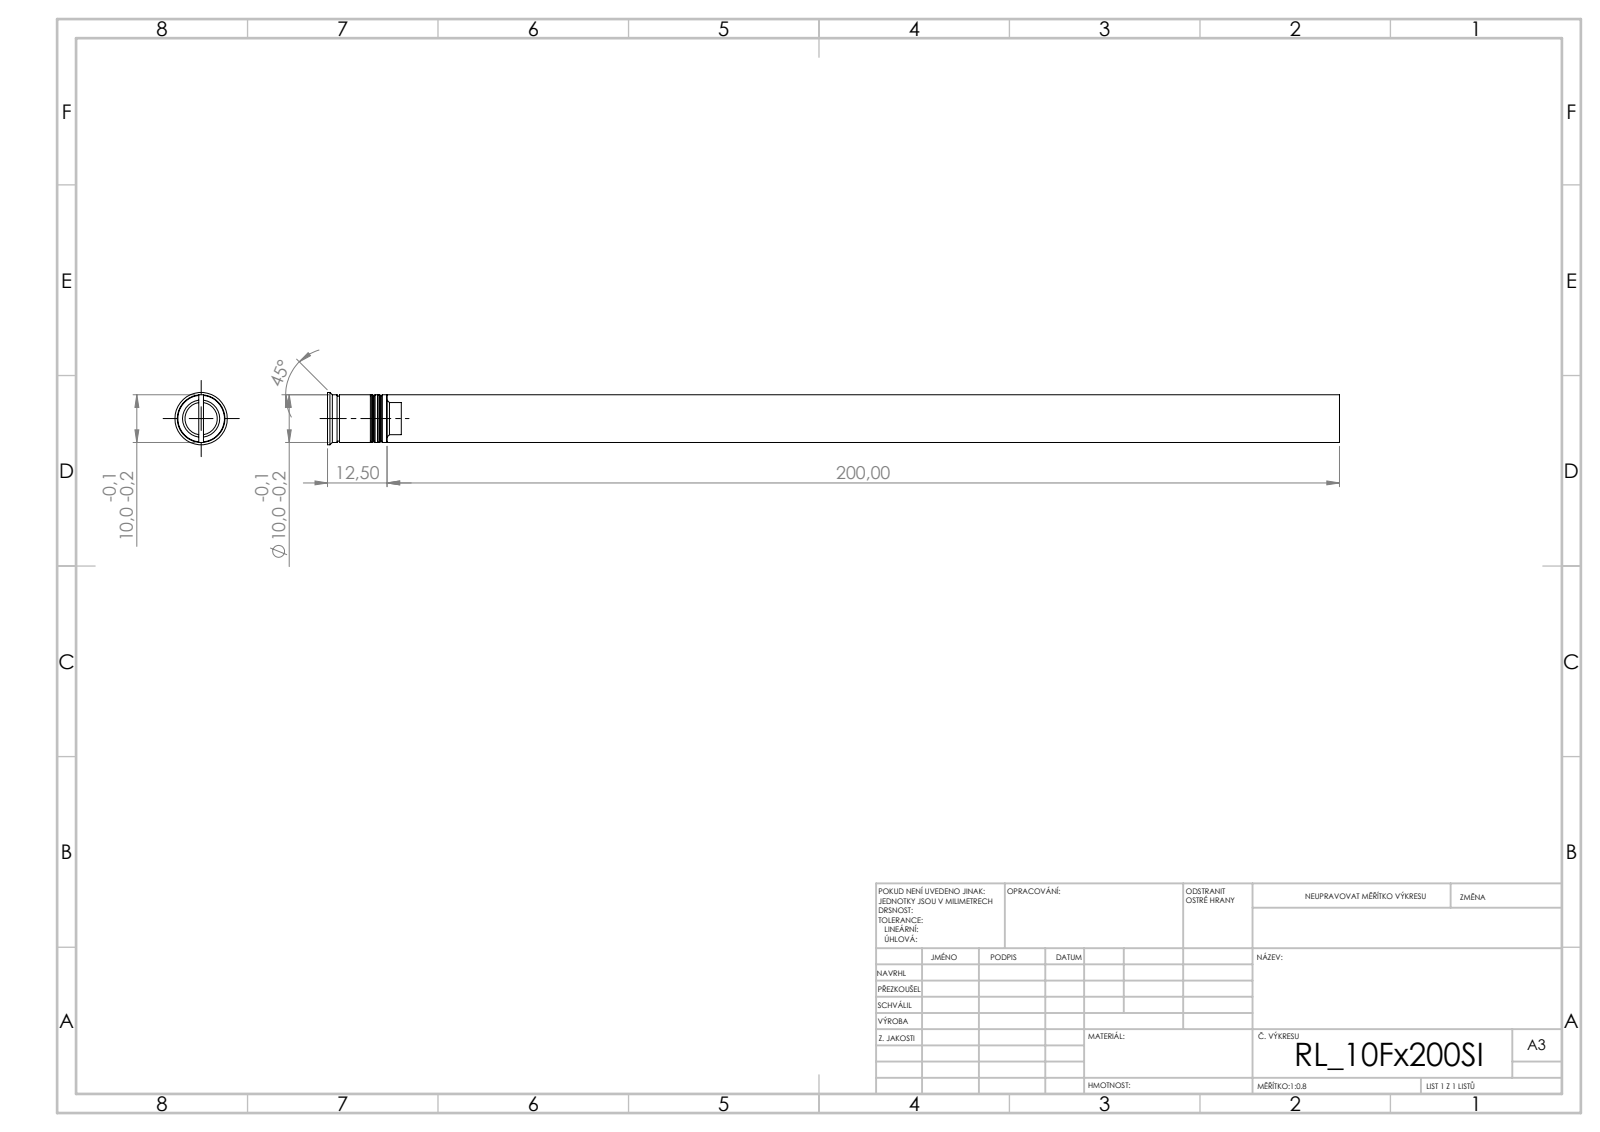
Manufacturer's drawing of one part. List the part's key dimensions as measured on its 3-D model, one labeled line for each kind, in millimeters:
STEP written by: SolidWorks 2019 (CONFIG_CONTROL_DESIGN)
Units: millimetres
Bodies: 3 solids, 88 faces (40 planar, 23 cylindrical, 25 other)
Overall size (bounding box): 212.5 × 11 × 11
Volume: 3 125 mm³ · Surface area: 5 429 mm²
Round bosses / shafts (diameter × count): ⌀11 ×1, ⌀10 ×1, ⌀9.4 ×1, ⌀7 ×1, ⌀6.8 ×1
Main face-to-face distances: 1, 10, 1.5, 0.7, 2.2, 0.8, 8, 8.7, 10.2, 9.5
